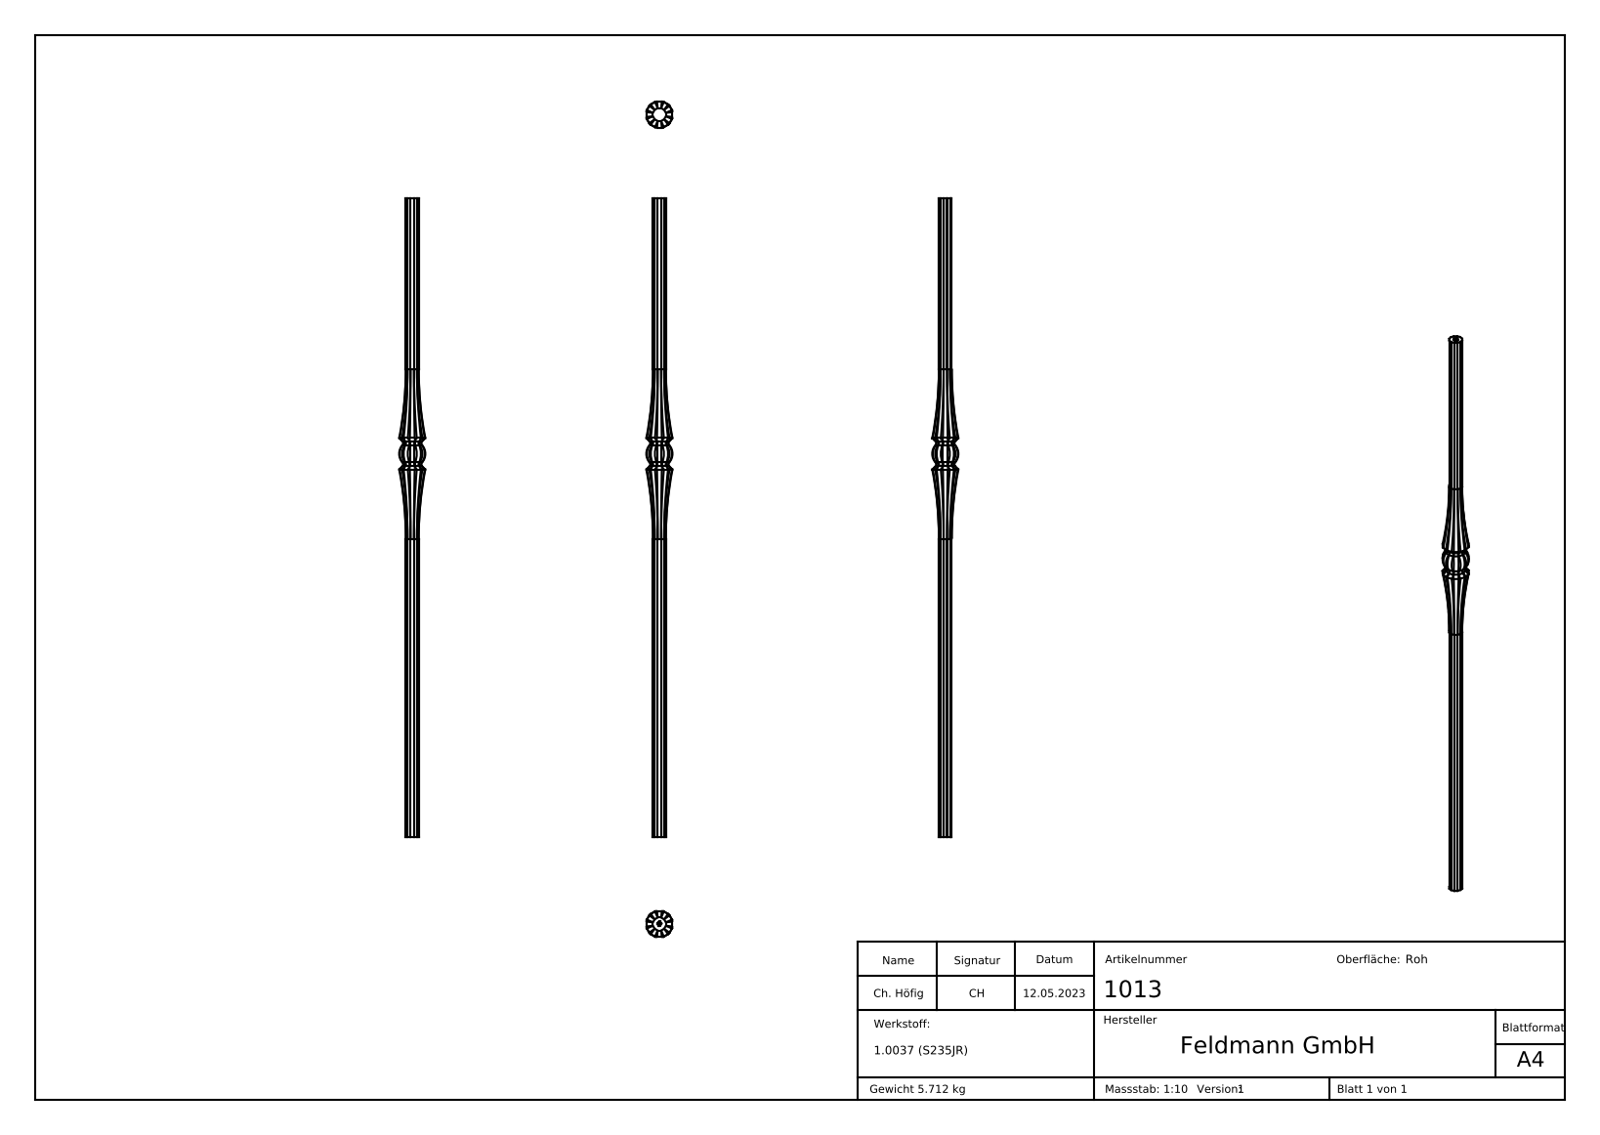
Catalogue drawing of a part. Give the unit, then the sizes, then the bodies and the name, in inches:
Units: inches
Overall size (bounding box): 47.244 × 1.937 × 1.937
Partial cylindrical surfaces — rounded edges, fillets, slot ends (radius × count): R0.213 ×24, R26.876 ×24, R0.969 ×6, R0.492 ×1
Main face-to-face distances: 0.953, 0.277, 47.244, 47.24, 0.28, 0.673, 0.394, 0.049, 0.022, 0.044
Volume: 44.69 in³ · Surface area: 164.1 in²
Bodies: 1 solid, 465 faces (206 planar, 84 cylindrical, 175 other)
Part name (STEP PRODUCT): 1013
STEP written by: SolidWorks 2018 (CONFIG_CONTROL_DESIGN)
